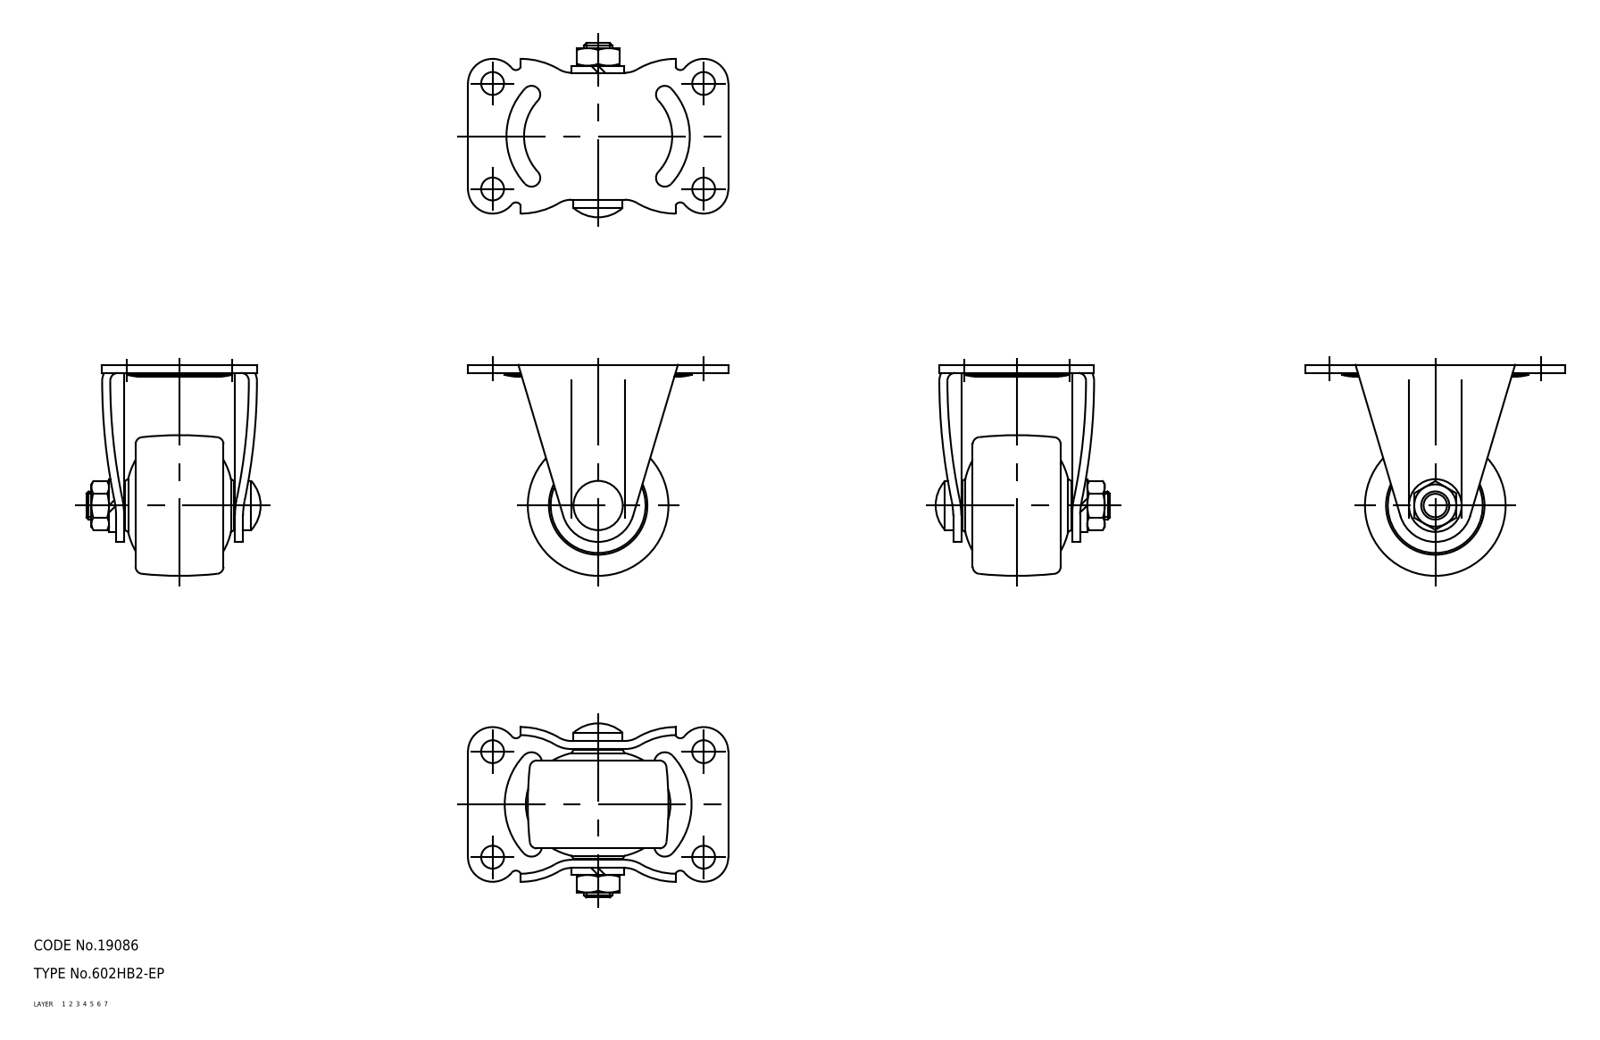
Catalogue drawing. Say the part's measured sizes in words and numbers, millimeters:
The part is named "wheel; axle; No_602HB2_EP_13810_36". Its 3-D file was written by "CADfix (AUTOMOTIVE_DESIGN)". It is 3 solids with 183 faces: 0 planar, 0 cylindrical and 183 other. Overall it measures 74 by 60 by 49.5 millimeters. Its volume is 46 437 cubic millimeters and its surface area 21 349 square millimeters.
